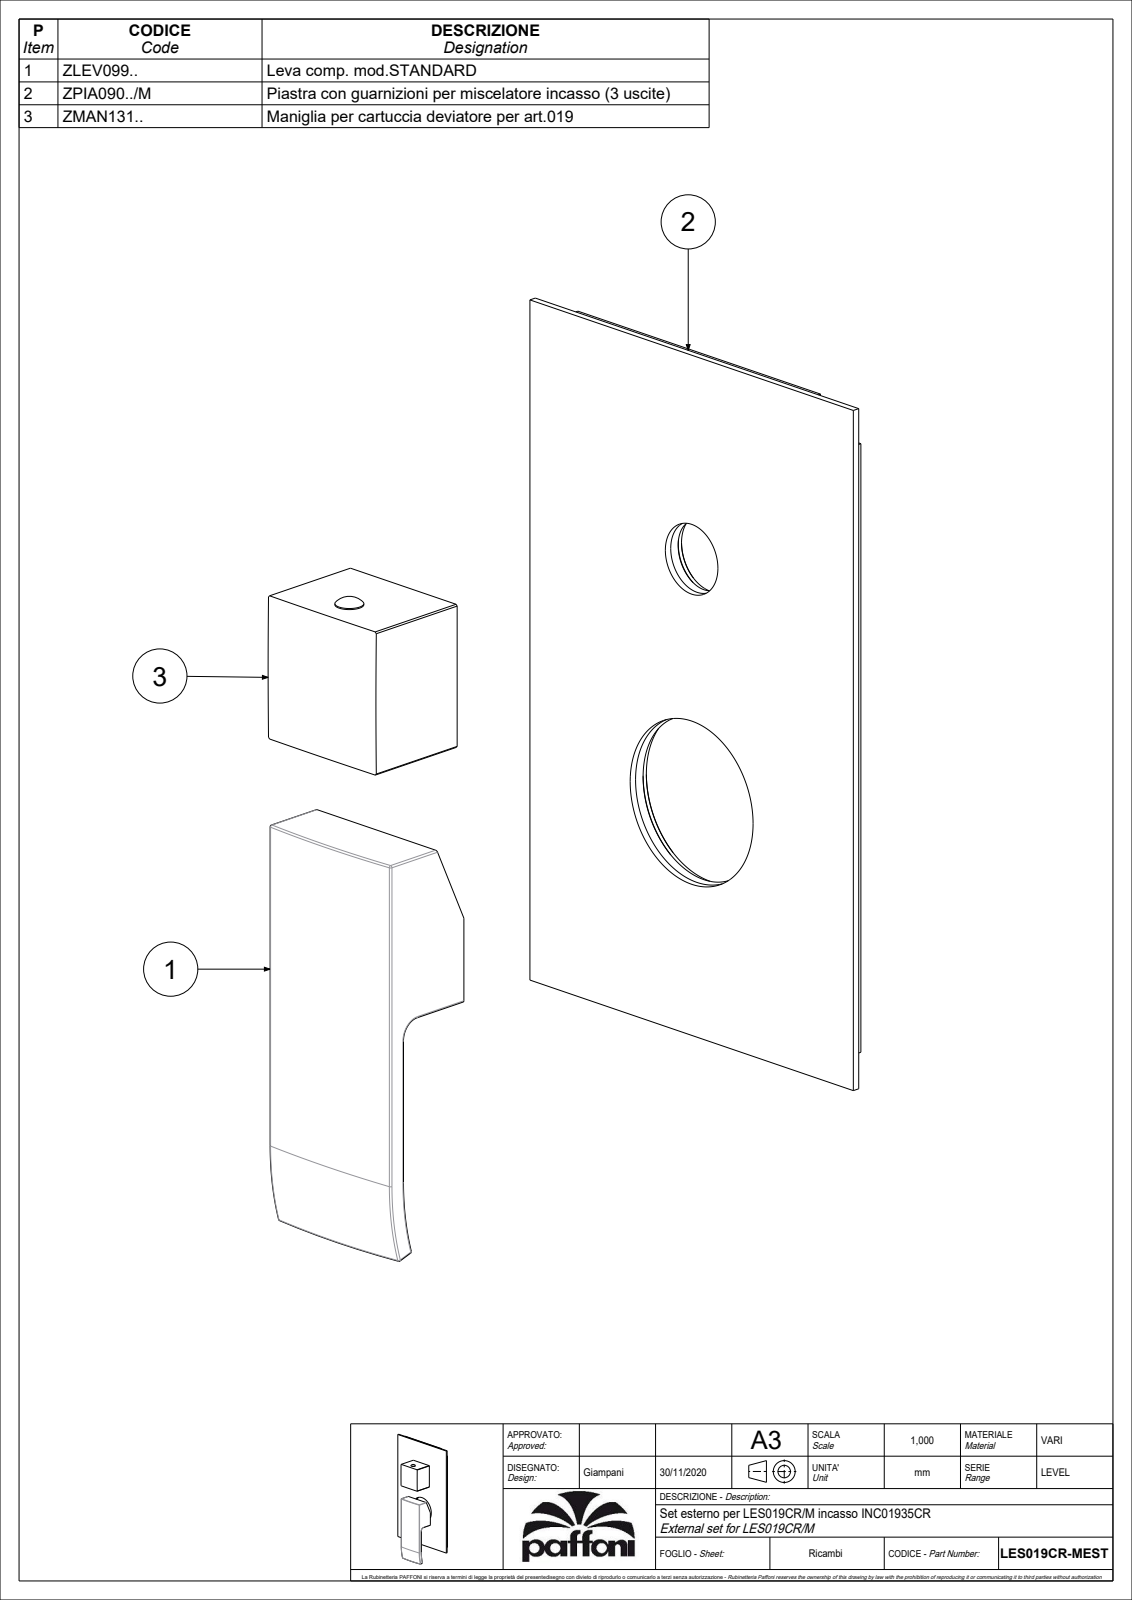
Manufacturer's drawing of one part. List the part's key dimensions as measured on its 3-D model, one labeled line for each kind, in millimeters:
Part name (STEP PRODUCT): LES018CR-MEST
STEP written by: CREO PARAMETRIC BY PTC INC, 2020044 (CONFIG_CONTROL_DESIGN)
Units: millimetres
Bodies: 3 solids, 279 faces (111 planar, 105 cylindrical, 63 other)
Overall size (bounding box): 212.38 × 120 × 39.99
Volume: 110 539 mm³ · Surface area: 82 574 mm²
Round holes (diameter × count): ⌀3 ×2, ⌀5.5 ×2, ⌀3.2 ×1, ⌀3.3 ×1, ⌀4.2 ×1, ⌀7.8 ×1, ⌀14.8 ×1, ⌀19.5 ×1, ⌀21.5 ×1, ⌀25 ×1, ⌀36 ×1, ⌀45.6 ×1
Round bosses / shafts (diameter × count): ⌀7.6 ×2, ⌀54.6 ×1, ⌀28.5 ×1, ⌀5 ×1
Partial cylindrical surfaces — rounded edges, fillets, slot ends (radius × count): R1.5 ×14, R0.5 ×10, R2 ×4, R300 ×2, R2.25 ×1, R28 ×1
Main face-to-face distances: 2, 2.8, 0.8, 40, 42.5, 2.5, 45, 30, 37.5, 29.2
Hole centre spacings: 7, 10, 58, 68
